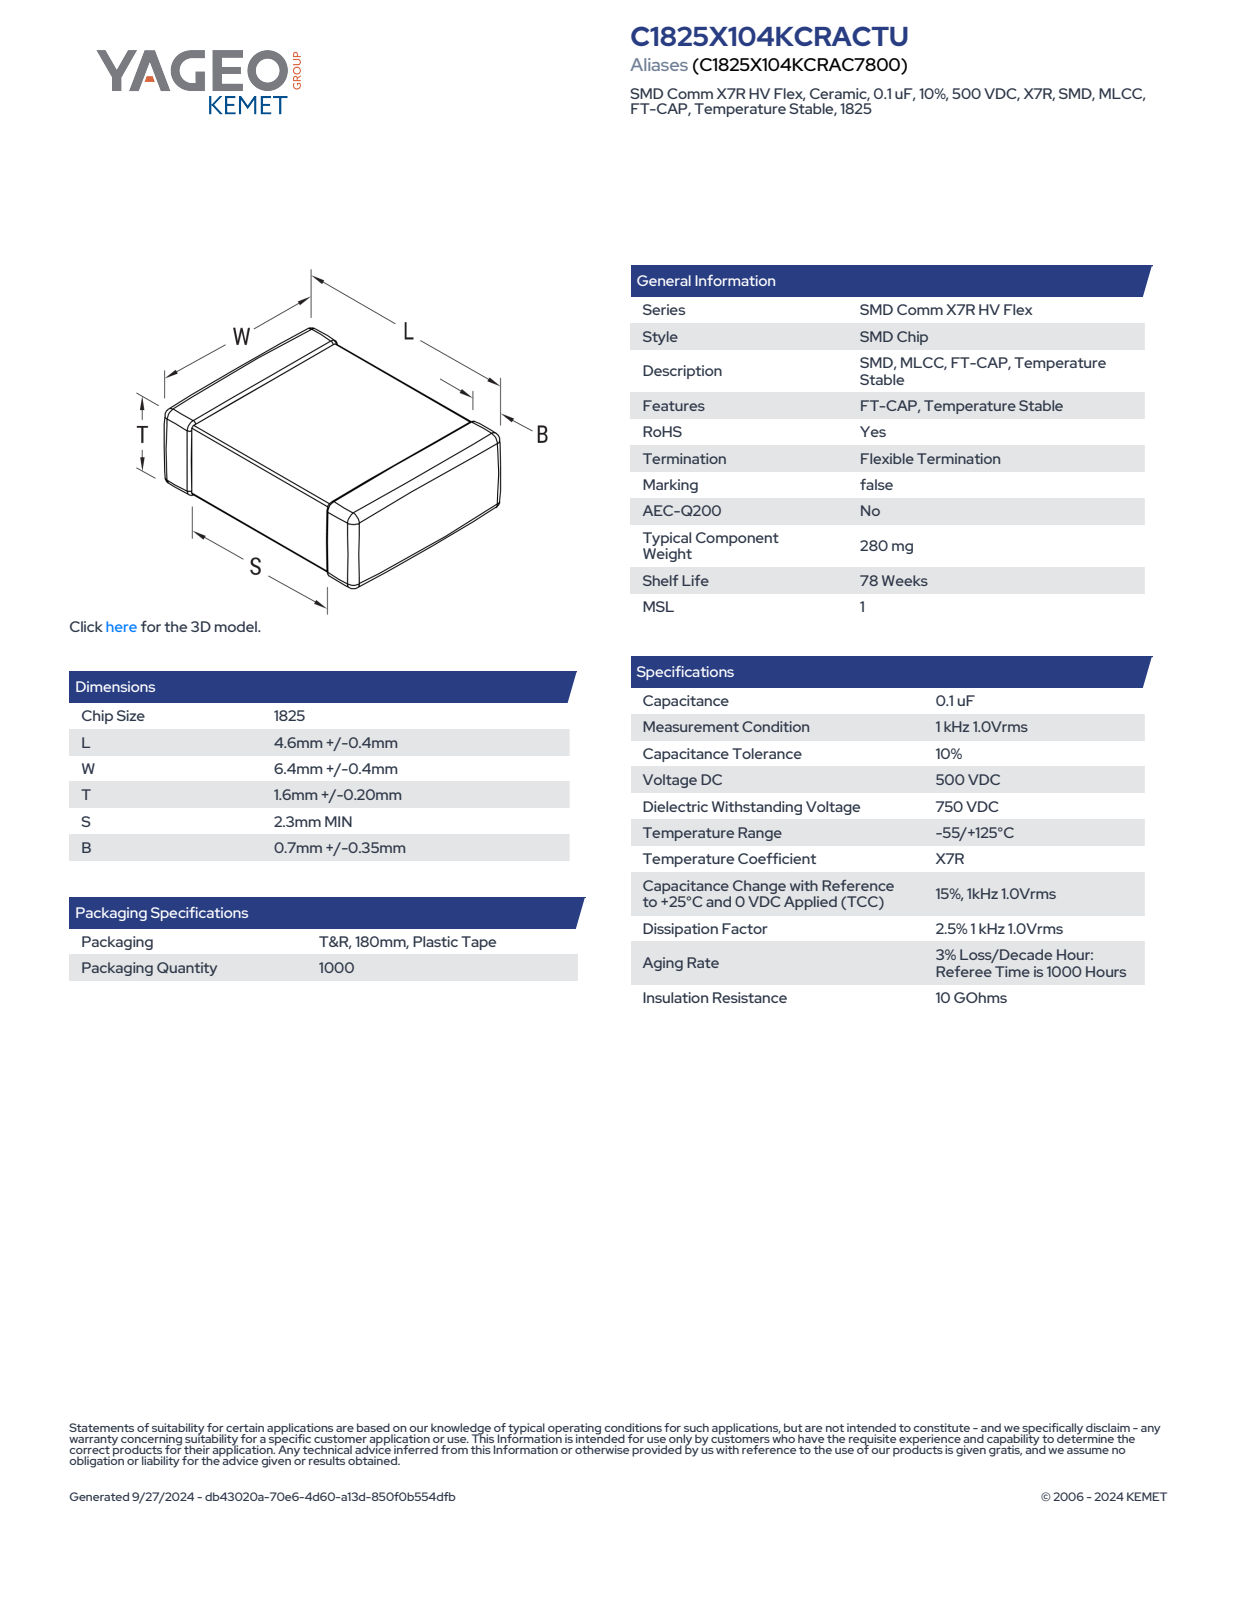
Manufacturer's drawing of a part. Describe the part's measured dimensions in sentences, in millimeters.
The part is named "CCS_CCSTDNOS_1825_L5W6.8T1.8B1.05". Its 3-D file was written by "SolidWorks 2014 (AUTOMOTIVE_DESIGN)". It is 4 solids with 121 faces: 71 planar, 34 cylindrical and 16 other. Overall it measures 6.8 by 5 by 1.8 millimeters. Its volume is 54 cubic millimeters and its surface area 107 square millimeters. Partial cylindrical surfaces (rounded edges, fillets, slot ends): 24 of radius 0.14. The main face-to-face distances are 1.66, 1.52, 1.8, 5, 6.66, 6.52, 6.8, 3.54, 3.12, 0.36.
